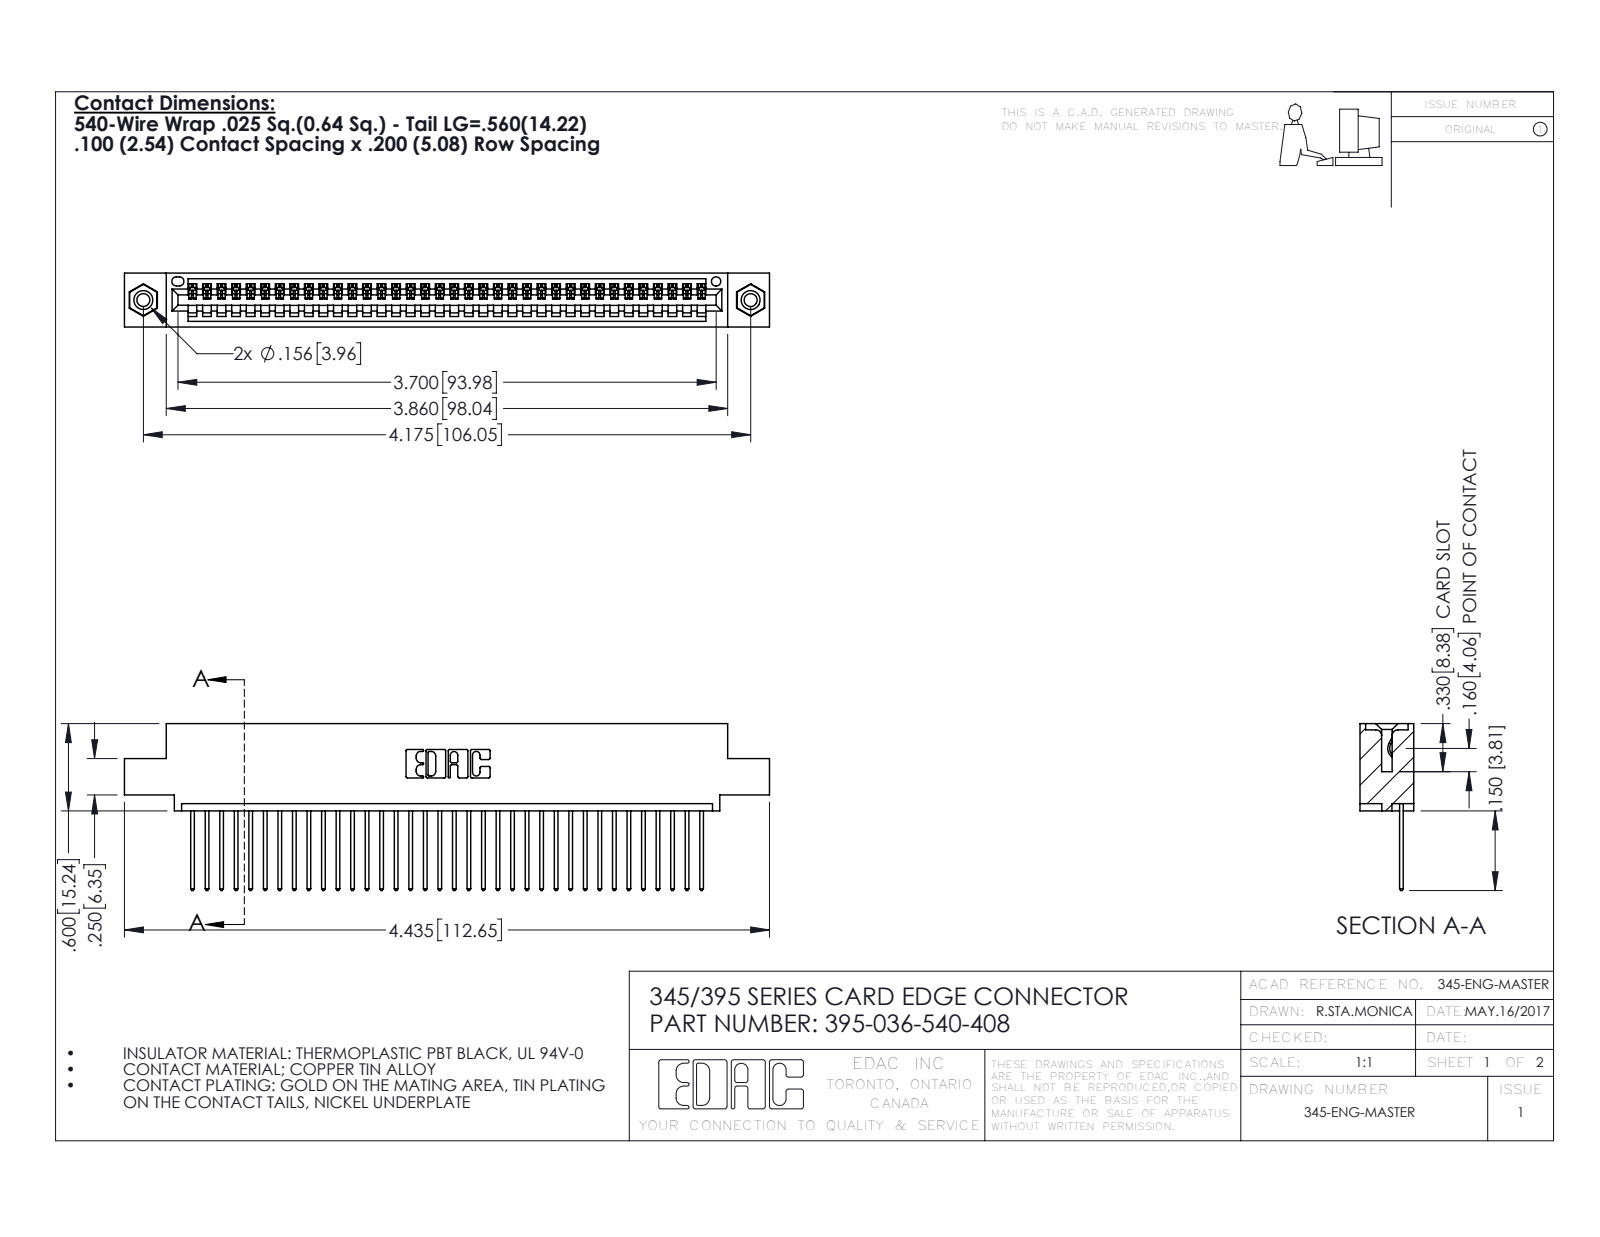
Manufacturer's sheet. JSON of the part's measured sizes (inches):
{"part_name": "345 Part_0.110 Offset - 0.156 Dia-TI; 345-250-001_345-250-003-102; 395-036-540-408; 345-292-001_345-293-140", "step_written_by": "SolidWorks 2016 (CONFIG_CONTROL_DESIGN)", "units": "inches", "bodies": {"solids": 39, "faces": 2278, "planar": 1556, "cylindrical": 706, "other": 16}, "overall_size": [4.435, 1.147, 0.37], "volume_in3": 0.648, "surface_area_in2": 22.45, "round_holes": [[0.089, 2], [0.125, 2], [0.156, 2], [0.064, 1]], "round_bosses_or_shafts": [[0.155, 2]], "partial_cylinders_radius": [[0.006, 72], [0.01, 72], [0.01, 22], [0.007, 6], [0.031, 6], [0.026, 3], [0.031, 2], [0.04, 2]], "face_to_face_distances": [0.072, 0.298, 0.37, 0.098, 0.272, 0.025, 0.2, 0.225, 0.149, 0.072], "hole_center_spacings": [0.27, 3.939, 4.175]}
